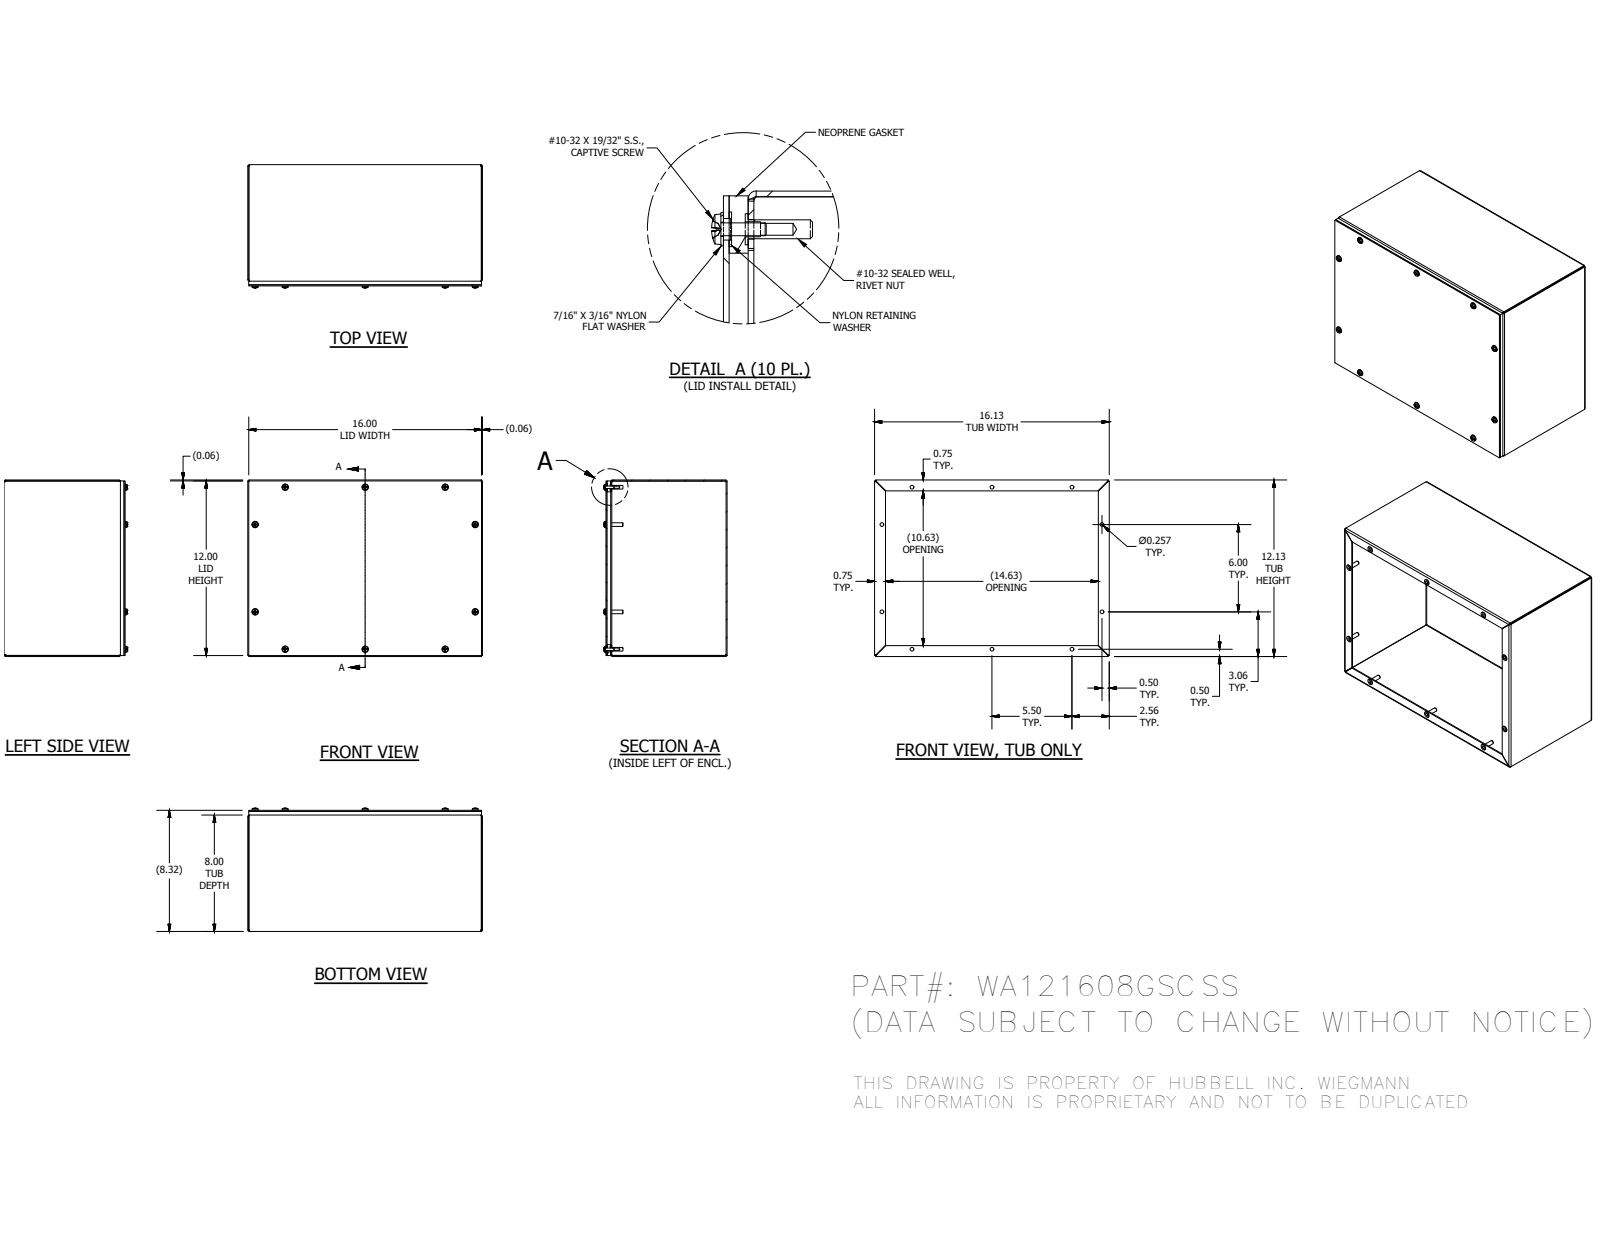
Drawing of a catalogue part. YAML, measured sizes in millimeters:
part_name: "WA121608GSCSSBKP; WA1216GSCSSLID; 37210; 39035 (+4 more)"
step_written_by: "Autodesk Inventor 2016 (AUTOMOTIVE_DESIGN)"
units: millimeters
bodies: {solids: 43, faces: 902, planar: 494, cylindrical: 182, other: 226}
overall_size: [409.57, 307.98, 215.35]
volume: 1218000
surface_area: 1207000
round_holes:
  - {diameter: 3.96, count: 10}
  - {diameter: 4.78, count: 10}
  - {diameter: 4.98, count: 10}
  - {diameter: 6.53, count: 10}
  - {diameter: 7.06, count: 10}
  - {diameter: 7.14, count: 10}
round_bosses_or_shafts:
  - {diameter: 11.51, count: 10}
  - {diameter: 11.11, count: 10}
  - {diameter: 10.31, count: 10}
  - {diameter: 6.3, count: 10}
  - {diameter: 4.25, count: 10}
partial_cylinders:
  - {radius: 0.79, count: 12}
  - {radius: 2.27, count: 10}
  - {radius: 1.78, count: 8}
  - {radius: 2.67, count: 8}
face_to_face_distances: [1.88, 209.55, 306.1, 207.67, 211.43, 407.7, 307.98, 304.22, 201.32, 8.23]
hole_center_spacings: [83.55, 139.7, 202.82, 223.71, 290.17, 315.23, 338.11, 396.72]
